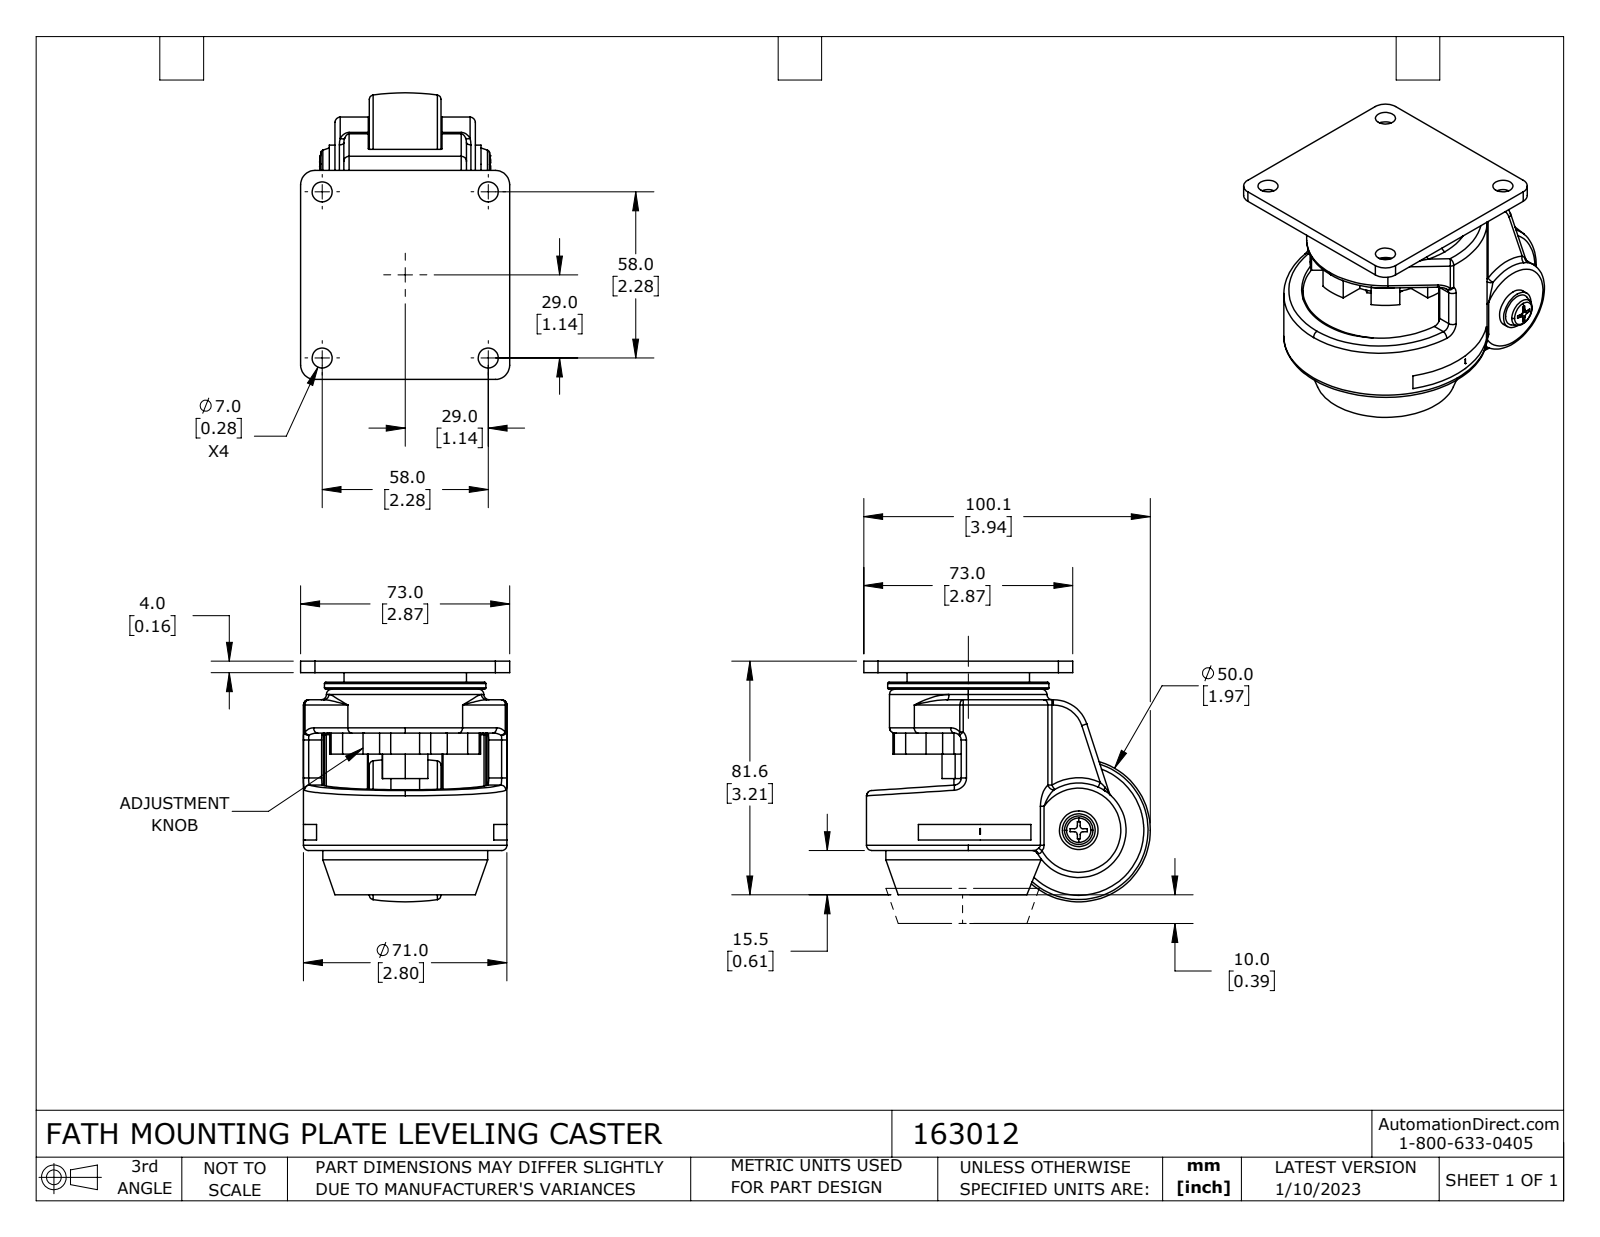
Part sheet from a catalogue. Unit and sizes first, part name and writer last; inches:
Units: inches
Overall size (bounding box): 3.94 × 3.307 × 2.874
Round holes (diameter × count): ⌀0.276 ×4, ⌀0.394 ×1, ⌀0.405 ×1, ⌀2.305 ×1
Round bosses / shafts (diameter × count): ⌀2.266 ×1, ⌀2.218 ×1, ⌀1.683 ×1, ⌀0.531 ×1, ⌀0.315 ×1
Partial cylindrical surfaces — rounded edges, fillets, slot ends (radius × count): R0.072 ×18, R0.024 ×16, R0.039 ×4, R0.197 ×4, R0.023 ×2, R0.096 ×2, R0.241 ×2, R0.482 ×1
Main face-to-face distances: 0.157, 0.998, 1.607, 1.765, 0.014, 1.446, 0.472, 0.984, 3.054, 3.211
Hole centre spacings: 1.615, 2.283, 3.229
Volume: 16.64 in³ · Surface area: 93.62 in²
Bodies: 1 solid, 310 faces (98 planar, 113 cylindrical, 99 other)
Part name (STEP PRODUCT): 163012
STEP written by: SolidWorks 2021 (CONFIG_CONTROL_DESIGN)
